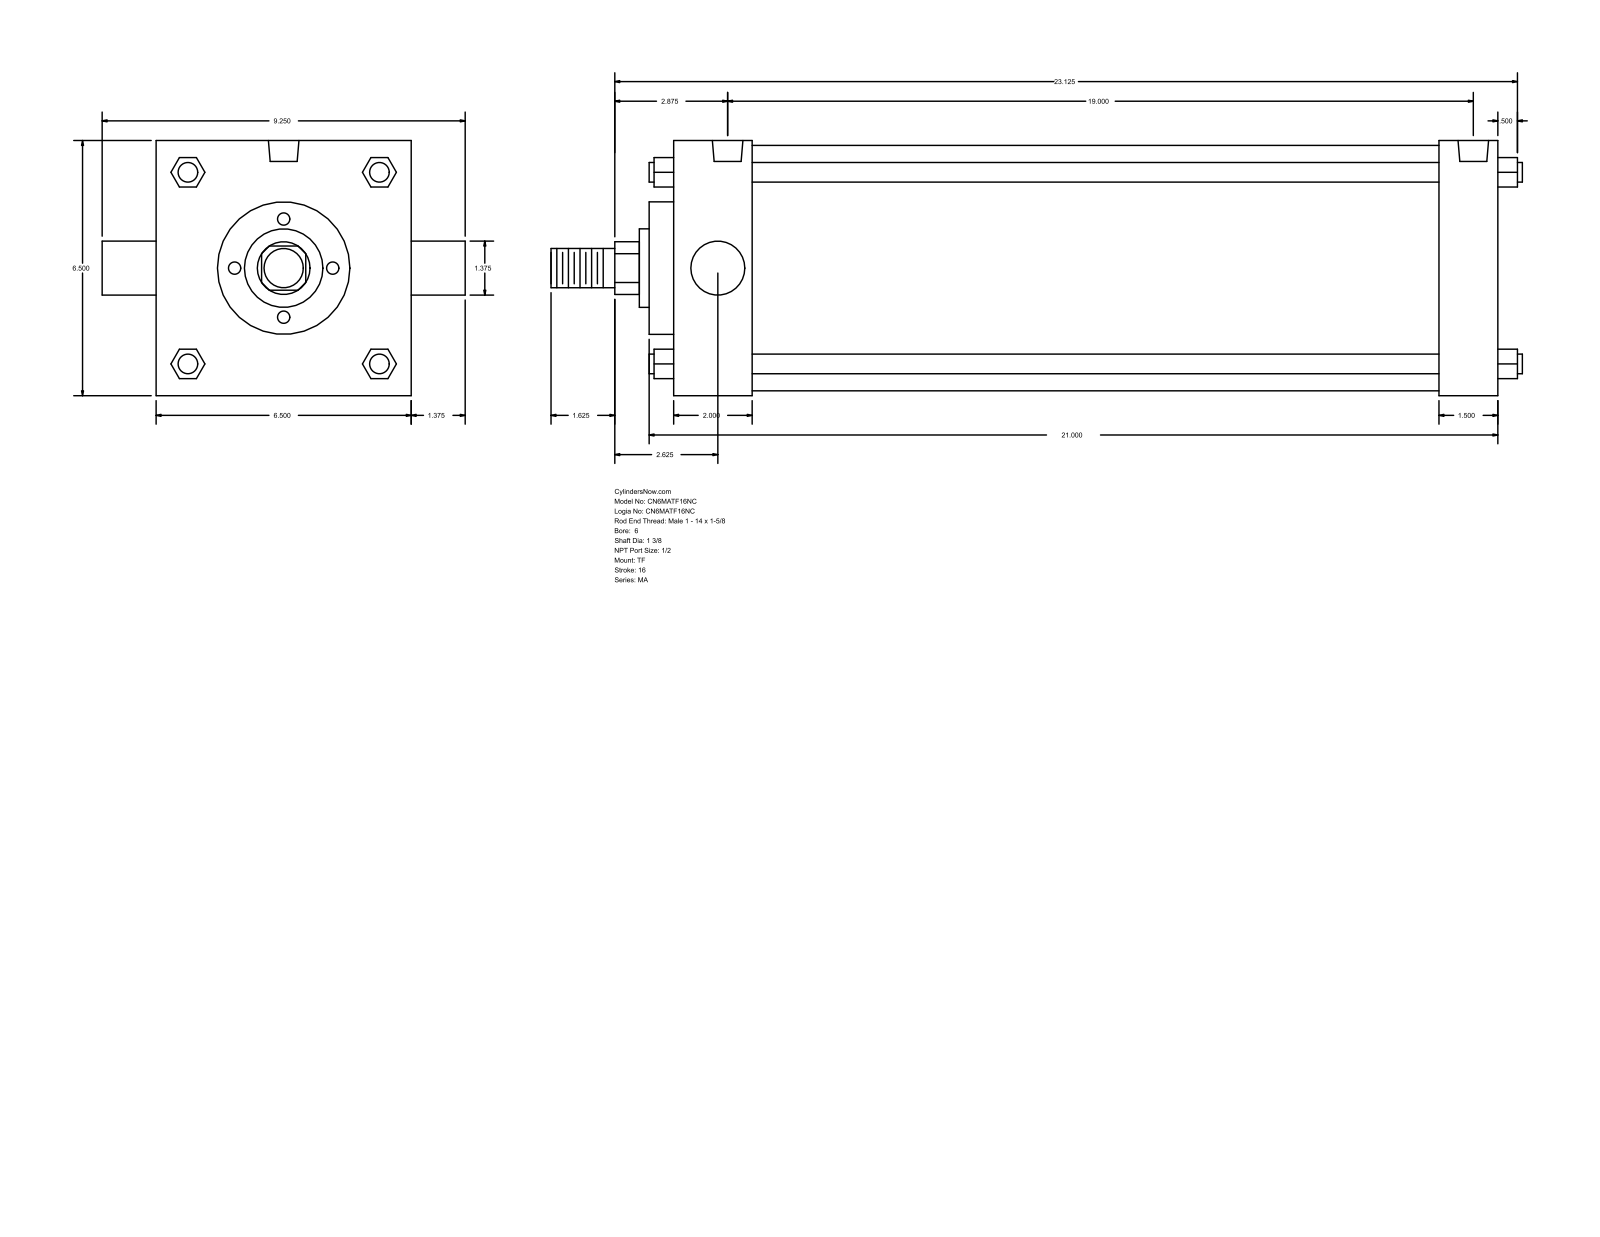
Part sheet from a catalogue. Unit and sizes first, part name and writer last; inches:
Units: inches
Overall size (bounding box): 24.75 × 9.25 × 6.5
Round holes (diameter × count): ⌀0.687 ×3, ⌀0.778 ×2
Round bosses / shafts (diameter × count): ⌀0.5 ×4, ⌀1.375 ×2, ⌀6.25 ×1, ⌀3.375 ×1, ⌀2 ×1, ⌀1 ×1
Partial cylindrical surfaces — rounded edges, fillets, slot ends (radius × count): R0.672 ×1
Main face-to-face distances: 6.5, 21.125, 2, 19.625, 19.125, 17.625, 1.5, 2.625, 0.625, 20.25
Hole centre spacings: 0.125, 19, 19.125
Bodies: 0 solids, 122 faces (93 planar, 29 cylindrical, 0 other)
Part name (STEP PRODUCT): MA_TF__0600_1.375
STEP written by: GSSL Pune (CONFIG_CONTROL_DESIGN)
